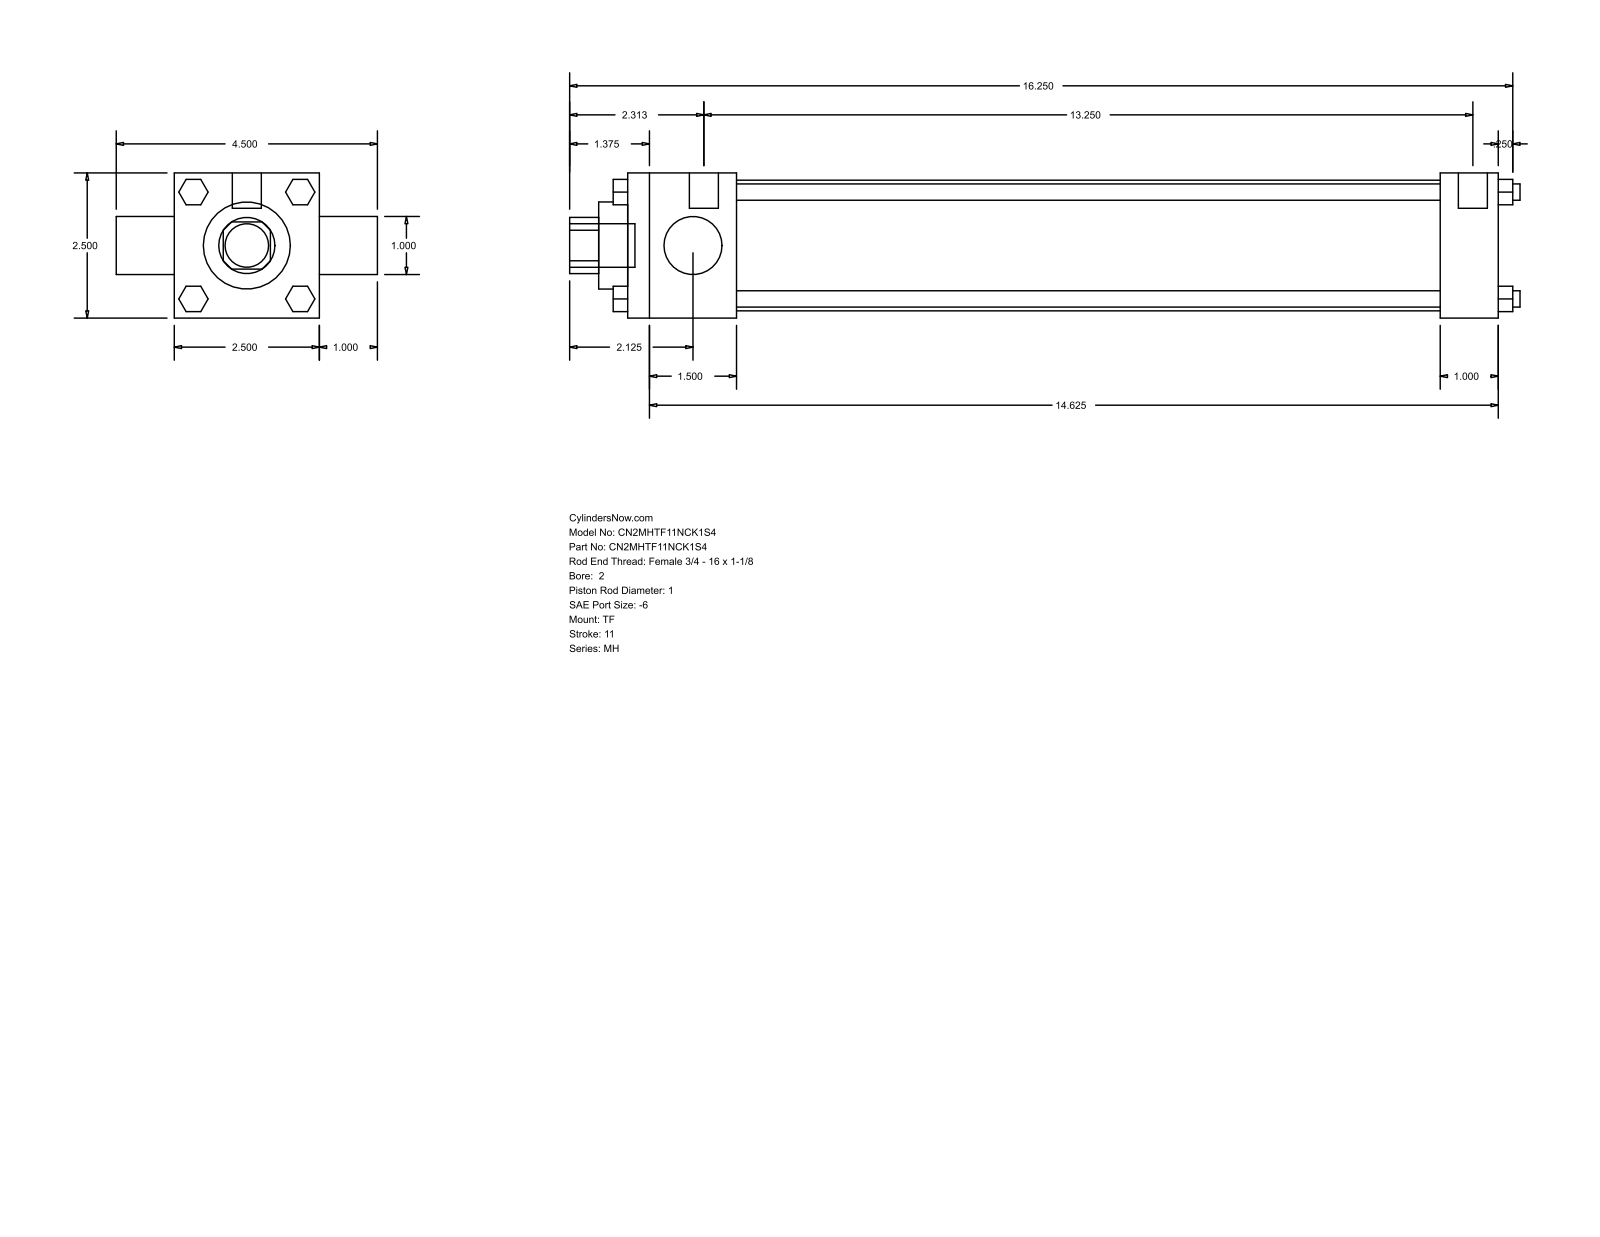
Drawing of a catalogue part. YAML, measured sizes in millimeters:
part_name: "MH_TF__0200_1"
step_written_by: "GSSL Pune (CONFIG_CONTROL_DESIGN)"
units: millimeters
bodies: {solids: 0, faces: 120, planar: 92, cylindrical: 28, other: 0}
overall_size: [415.93, 114.3, 63.5]
round_holes:
  - {diameter: 25.4, count: 2}
  - {diameter: 38.1, count: 1}
  - {diameter: 57.15, count: 1}
round_bosses_or_shafts:
  - {diameter: 7.14, count: 4}
  - {diameter: 5.56, count: 3}
  - {diameter: 12.7, count: 2}
  - {diameter: 19.05, count: 1}
partial_cylinders:
  - {radius: 12.29, count: 1}
face_to_face_distances: [63.5, 381, 25.4, 47.63, 355.6, 307.97, 333.37, 88.9, 393.7, 6.35]
